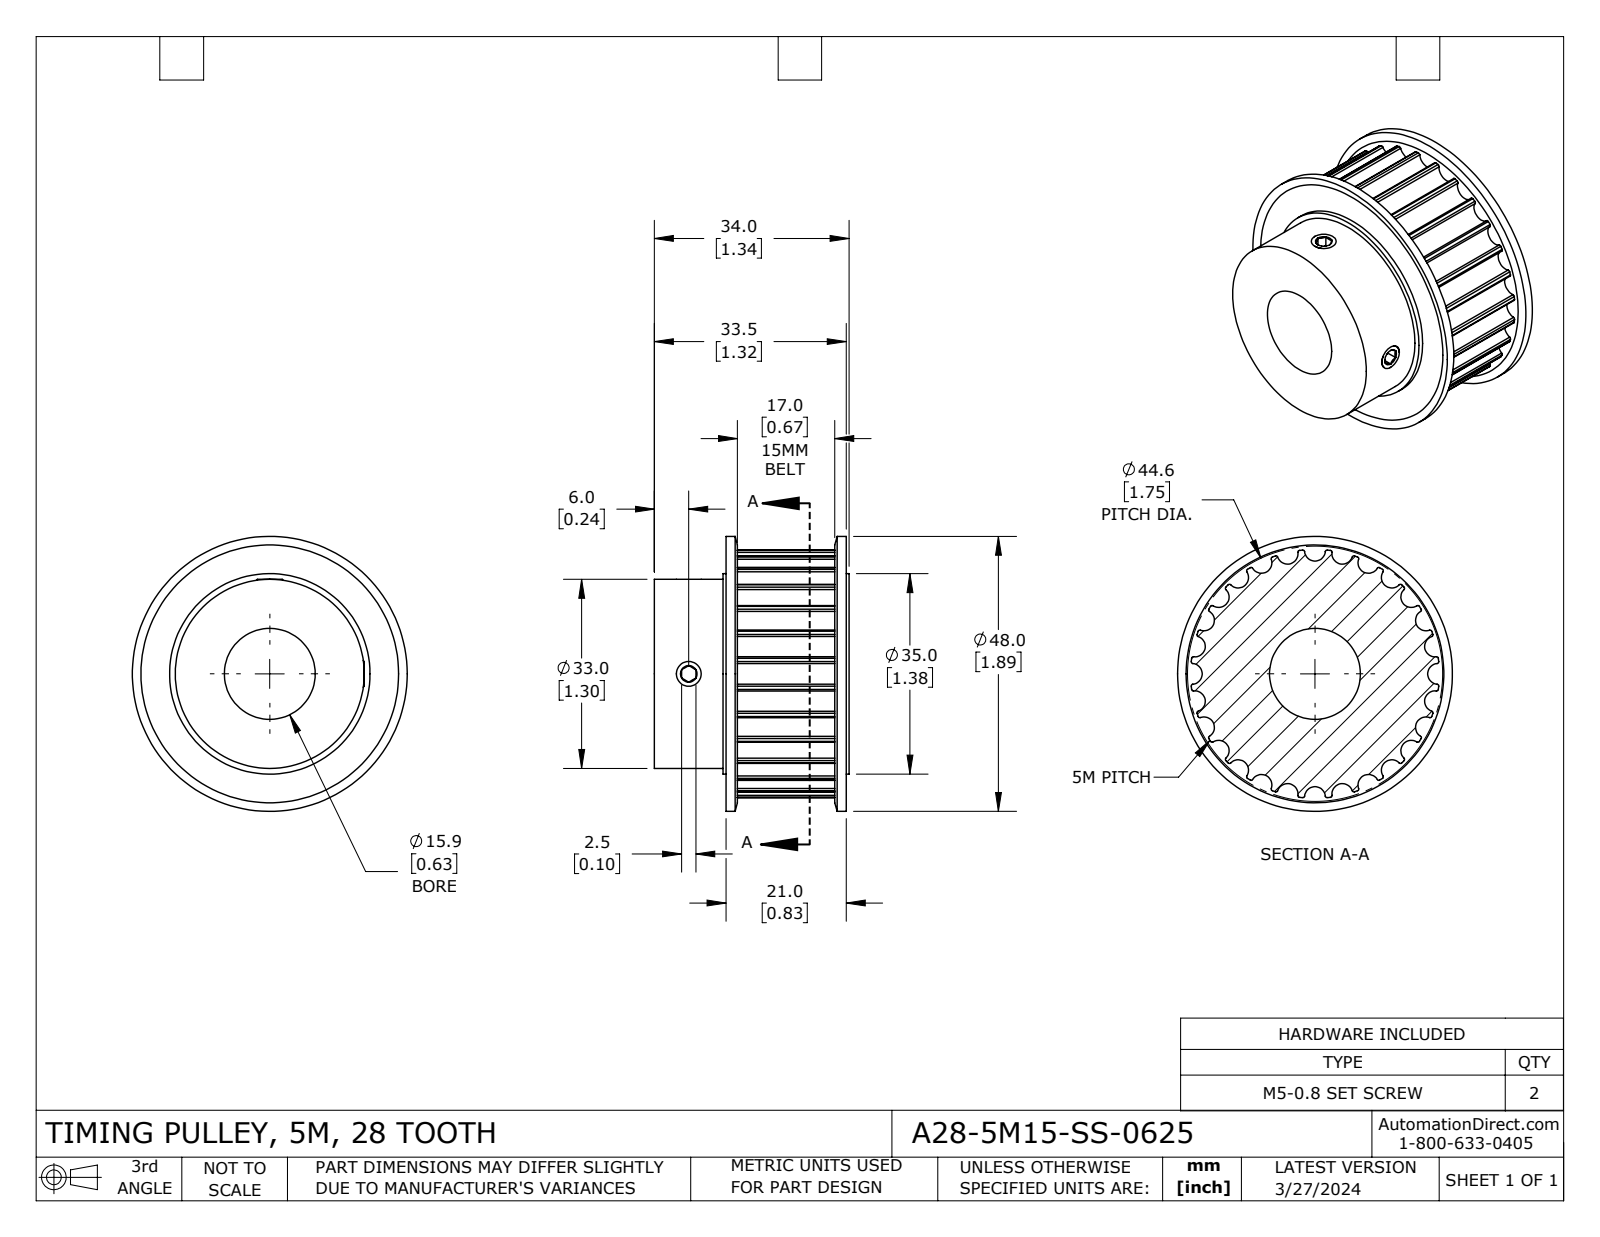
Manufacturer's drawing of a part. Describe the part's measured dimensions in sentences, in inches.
The part is named "A28-5M15-SS-0625". Its 3-D file was written by "SolidWorks 2021 (CONFIG_CONTROL_DESIGN)". It is 5 solids with 222 faces: 25 planar, 163 cylindrical and 34 other. Overall it measures 1.89 by 1.89 by 1.339 inches. Its volume is 2.033 cubic inches and its surface area 21.16 square inches. Round holes: 2 of diameter 0.165, 1 of diameter 0.625, 1 of diameter 1.378. Round bosses or shafts: 2 of diameter 0.197, 1 of diameter 1.89, 1 of diameter 1.299. Partial cylindrical surfaces (rounded edges, fillets, slot ends): 56 of radius 0.012, 28 of radius 0.072, 1 of radius 0.855. The main face-to-face distances are 0.063, 0.732, 0.669, 0.098, 0.768, 0.035, 0.831, 1.339, 1.24, 0.571.
